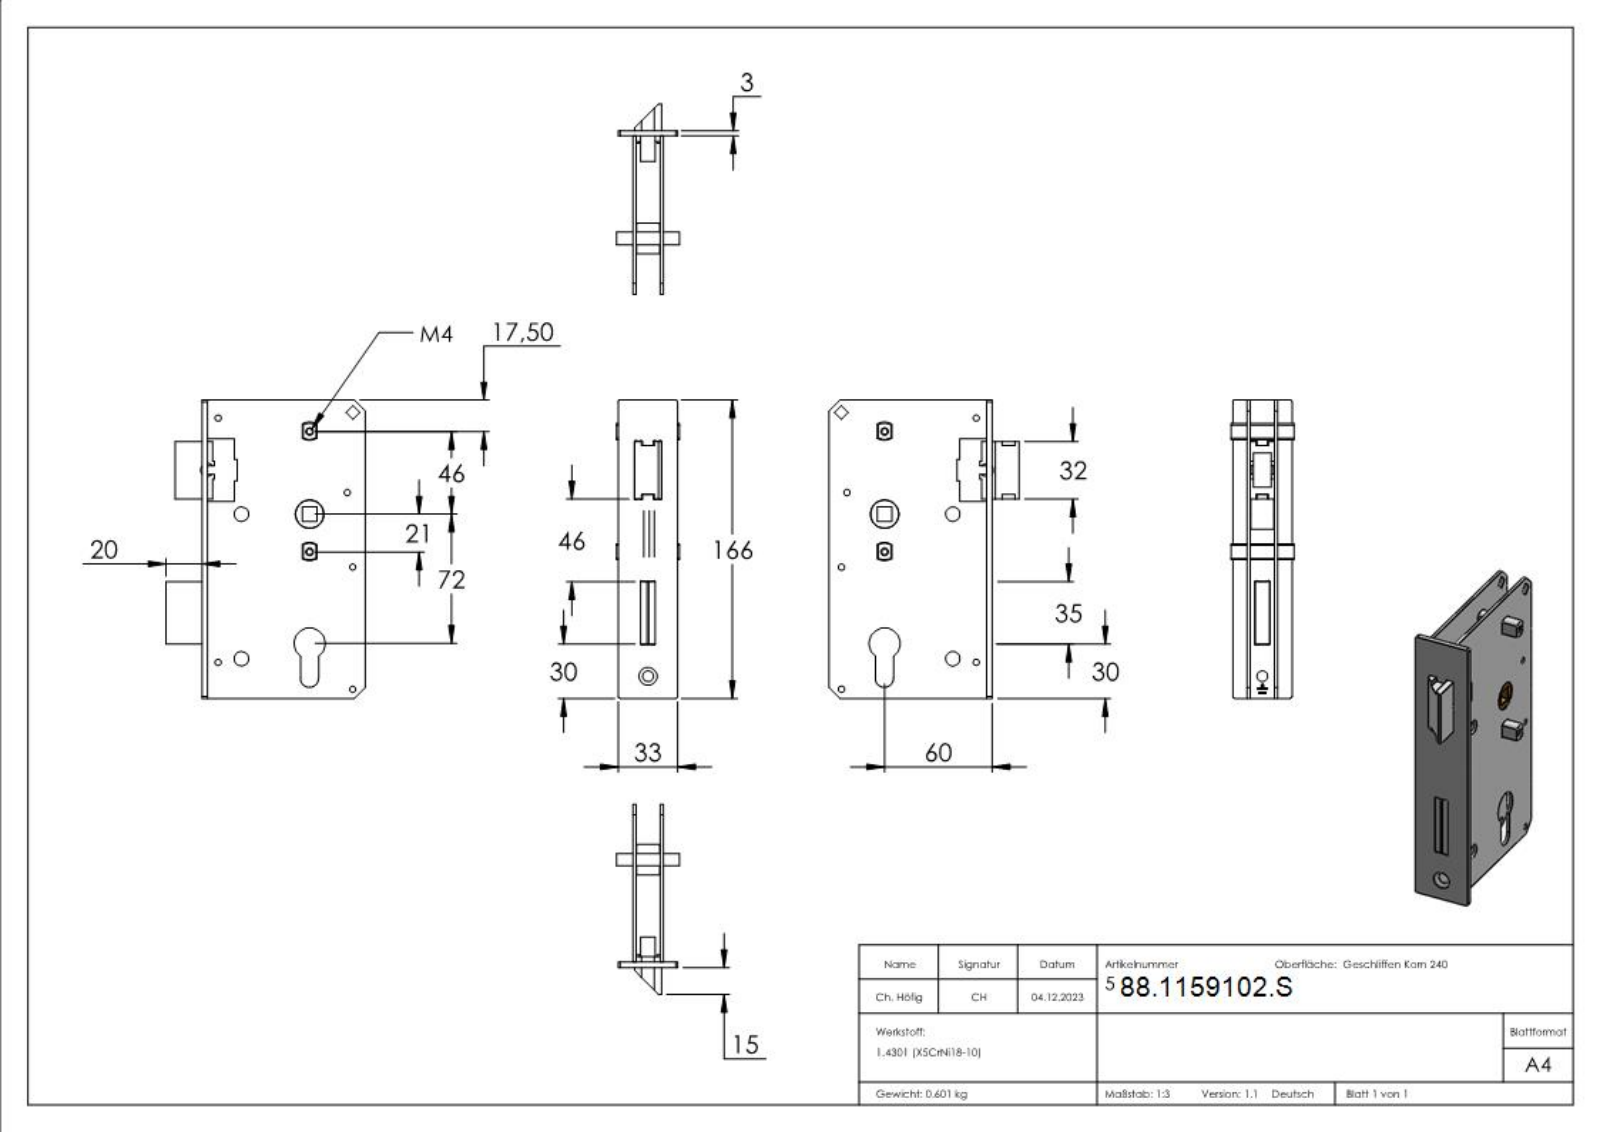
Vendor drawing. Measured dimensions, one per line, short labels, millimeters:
name: Schlosskasten Teil3 Konfig_59XXX-240 Teil3; Schlosskasten Teil5 Konfig_59XXX-240 Teil5; 59102-S; Schlosskasten Teil4 Konfig_59XXX-240 Teil4 (+1 more)
written by: SolidWorks 2018 (CONFIG_CONTROL_DESIGN)
unit: mm
bodies: 8 solids, 452 faces (253 planar, 71 cylindrical, 128 other)
size: 166 × 106 × 35
volume: 75 840 mm³; area: 76 109 mm²
holes: 5× ⌀3.5, 2× ⌀3.3, 2× ⌀8, 1× ⌀6, 1× ⌀10, 1× ⌀16, 1× ⌀17.3
bosses: 1× ⌀17, 1× ⌀15.5
rounds: 8× R0.3, 8× R0.6, 4× R0.5, 4× R1, 4× R4.39, 4× R7.5, 4× R8, 1× R2.4
face distances: 1.75, 15.25, 17, 13.5, 3, 8, 11.55, 9.75, 23.25, 25
hole spacings: 13.15, 21, 24.19, 25.46, 35.02, 38, 38.03, 38.94
